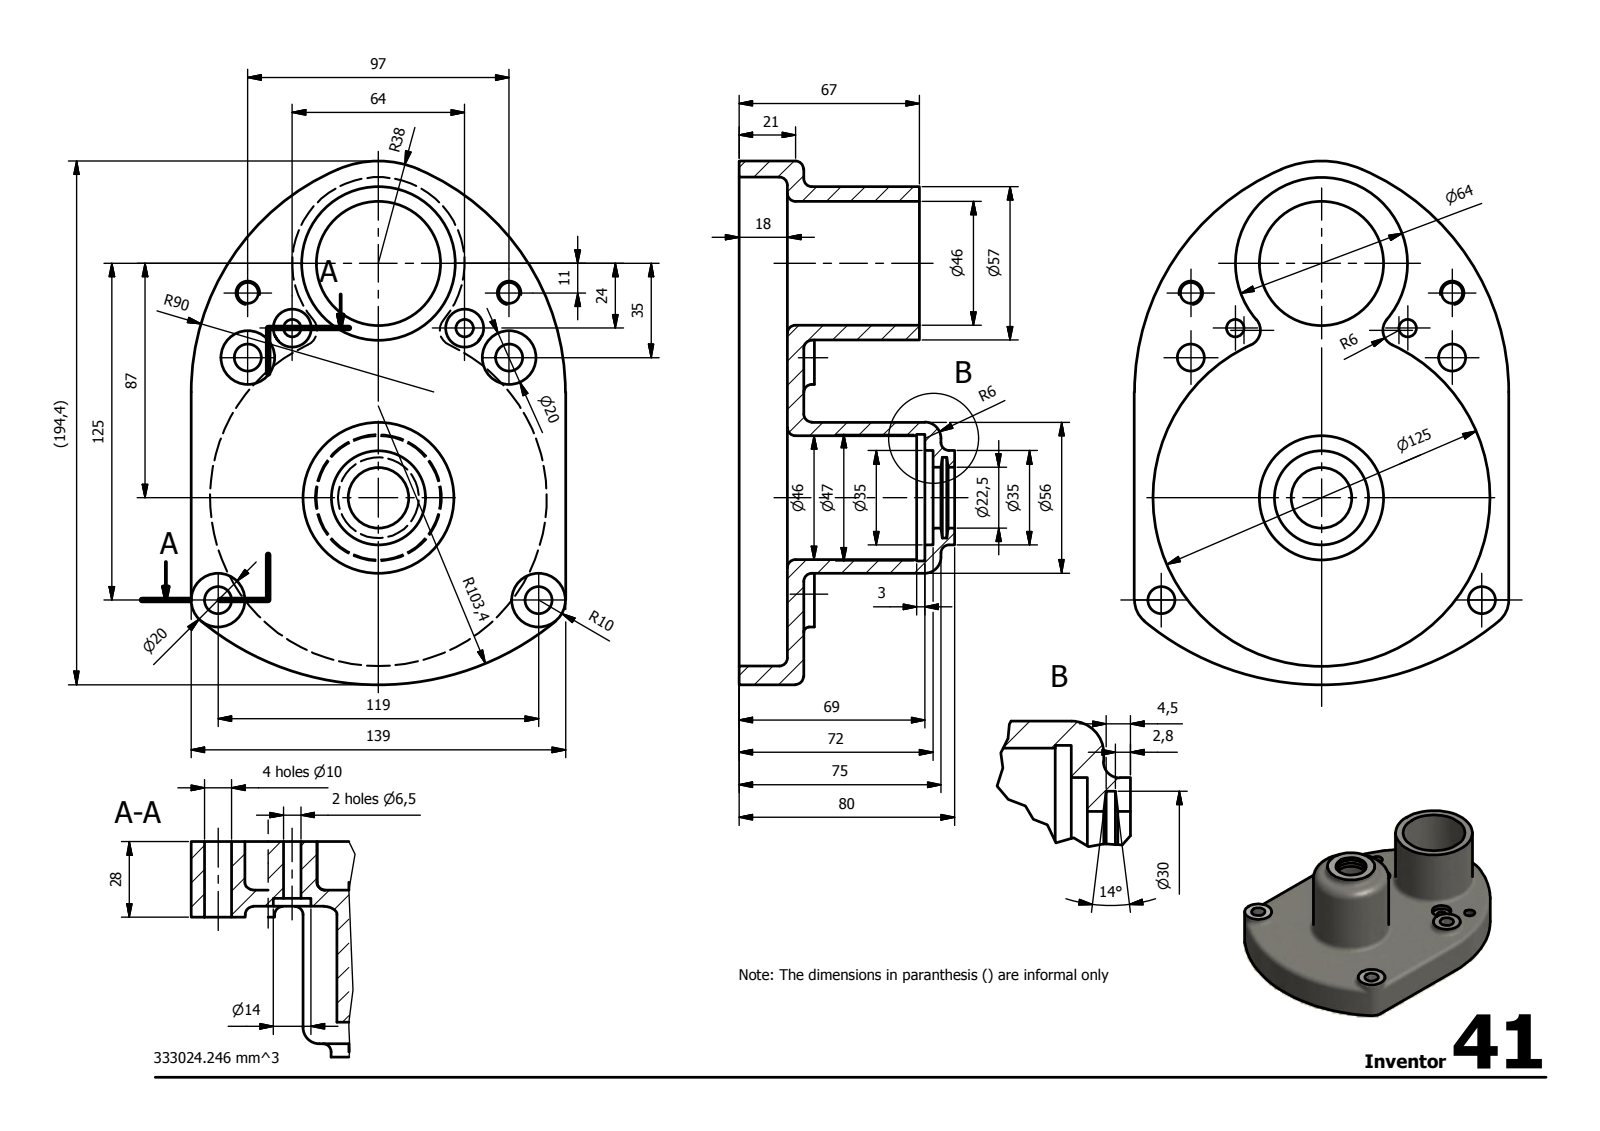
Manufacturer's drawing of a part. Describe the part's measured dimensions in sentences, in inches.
Its 3-D file was written by "Autodesk Inventor 2014 (AUTOMOTIVE_DESIGN)". It is 1 solid with 75 faces: 17 planar, 34 cylindrical and 24 other. Overall it measures 7.654 by 5.472 by 3.15 inches. Its volume is 20.32 cubic inches and its surface area 155.7 square inches. Round holes: 4 of diameter 0.394, 2 of diameter 0.256, 2 of diameter 0.301, 2 of diameter 0.551, 2 of diameter 1.811, 1 of diameter 0.886, 1 of diameter 1.181, 1 of diameter 1.378, 1 of diameter 1.85, 1 of diameter 4.921. Round bosses or shafts: 4 of diameter 0.787, 1 of diameter 2.244, 1 of diameter 2.205. Partial cylindrical surfaces (rounded edges, fillets, slot ends): 2 of radius 0.118, 2 of radius 0.236, 2 of radius 3.543, 1 of radius 1.26, 1 of radius 1.496, 1 of radius 4.071. The main face-to-face distances are 0.236, 0.709, 0.945, 5.472, 0.118, 2.008, 1.102, 0.394, 0.157, 2.638. The hole center spacings are 0.781, 0.827, 0.945, 1.575, 1.958, 2.355, 2.78, 2.782.
